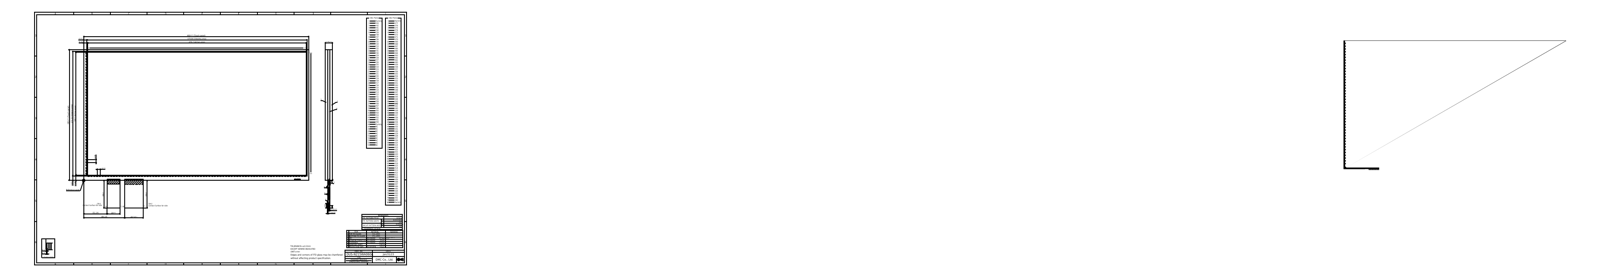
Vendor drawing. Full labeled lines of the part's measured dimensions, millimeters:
Part name (STEP PRODUCT): DUS-N215WA060A
STEP written by: Autodesk Inventor 2020 (AUTOMOTIVE_DESIGN)
Units: millimetres
Bodies: 1 solid, 568 faces (564 planar, 4 cylindrical, 0 other)
Overall size (bounding box): 686 × 402 × 2.35
Volume: 328 758 mm³ · Surface area: 291 251 mm²
Partial cylindrical surfaces — rounded edges, fillets, slot ends (radius × count): R0.2 ×4
Main face-to-face distances: 2.35, 1.2, 1.15, 1.25, 1.1, 285, 0.8, 1.55, 0.4, 490
